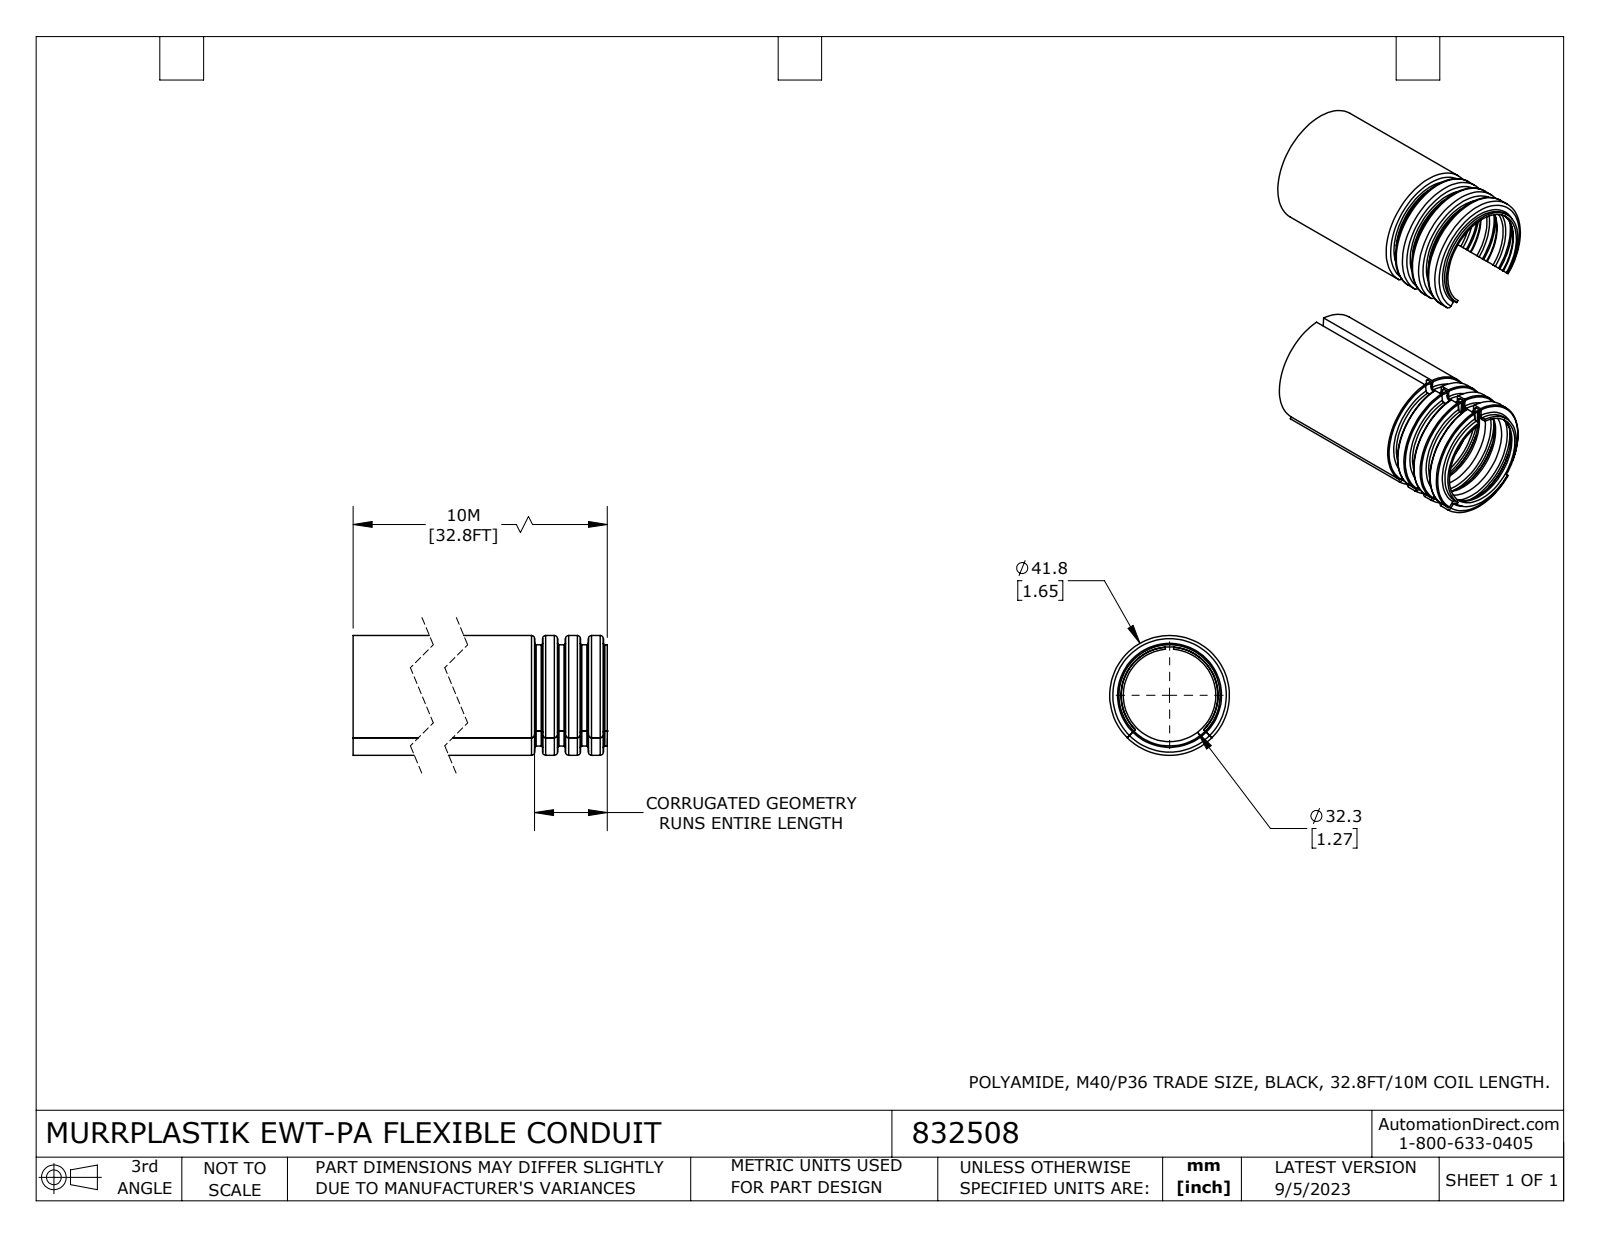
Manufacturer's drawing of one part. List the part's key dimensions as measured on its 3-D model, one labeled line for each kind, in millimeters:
Part name (STEP PRODUCT): 832508
STEP written by: SolidWorks 2021 (CONFIG_CONTROL_DESIGN)
Units: millimetres
Bodies: 2 solids, 335 faces (10 planar, 107 cylindrical, 218 other)
Overall size (bounding box): 80 × 41.8 × 41.8
Volume: 35 900 mm³ · Surface area: 41 970 mm²
Round holes (diameter × count): ⌀32.3 ×1, ⌀38.8 ×1
Round bosses / shafts (diameter × count): ⌀41.8 ×1, ⌀35.3 ×1
Partial cylindrical surfaces — rounded edges, fillets, slot ends (radius × count): R16.9 ×1, R20.1 ×1
Main face-to-face distances: 80
